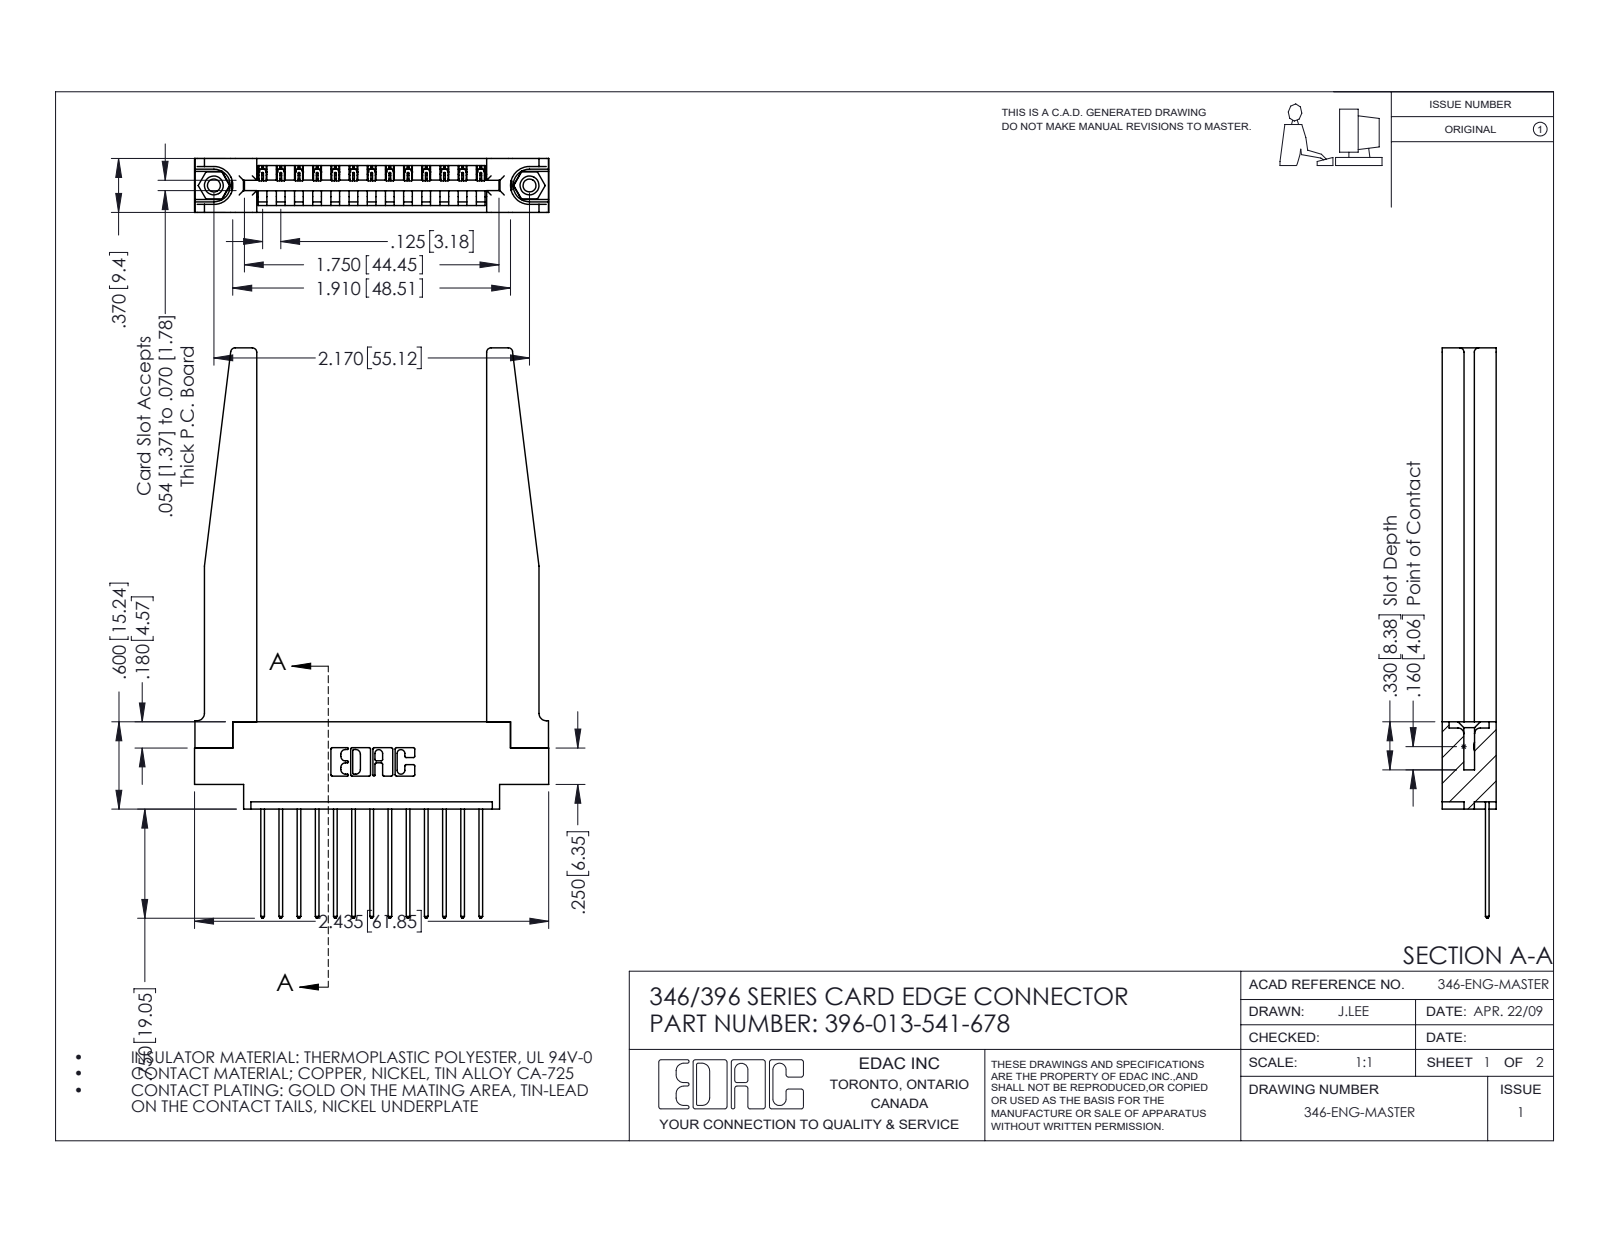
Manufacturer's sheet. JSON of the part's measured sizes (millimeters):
{"part_name": "345-292-001_345-293-141; 396-013-541-678; 346 Part_0.170 Offset - 0.156 Dia-TH; 346-220-078_345-220-078 (+1 more)", "step_written_by": "SolidWorks 2016 (CONFIG_CONTROL_DESIGN)", "units": "millimeters", "bodies": {"solids": 18, "faces": 1114, "planar": 742, "cylindrical": 320, "other": 52}, "overall_size": [99.6, 61.8, 9.4], "volume_mm3": 12500, "surface_area_mm2": 13650, "round_holes": [[2.3, 2], [3.2, 2], [4, 2], [1.6, 1]], "round_bosses_or_shafts": [[3.9, 2]], "partial_cylinders_radius": [[0.2, 26], [0.3, 26], [0.3, 22], [0.8, 8], [0.2, 6], [0.8, 6], [0.7, 3], [0.8, 2]], "face_to_face_distances": [9.4, 3.8, 1.8, 1.2, 8.2, 3.8, 6.4, 2.6, 5.6, 4.4], "hole_center_spacings": [6.2, 49.9, 55.1]}
